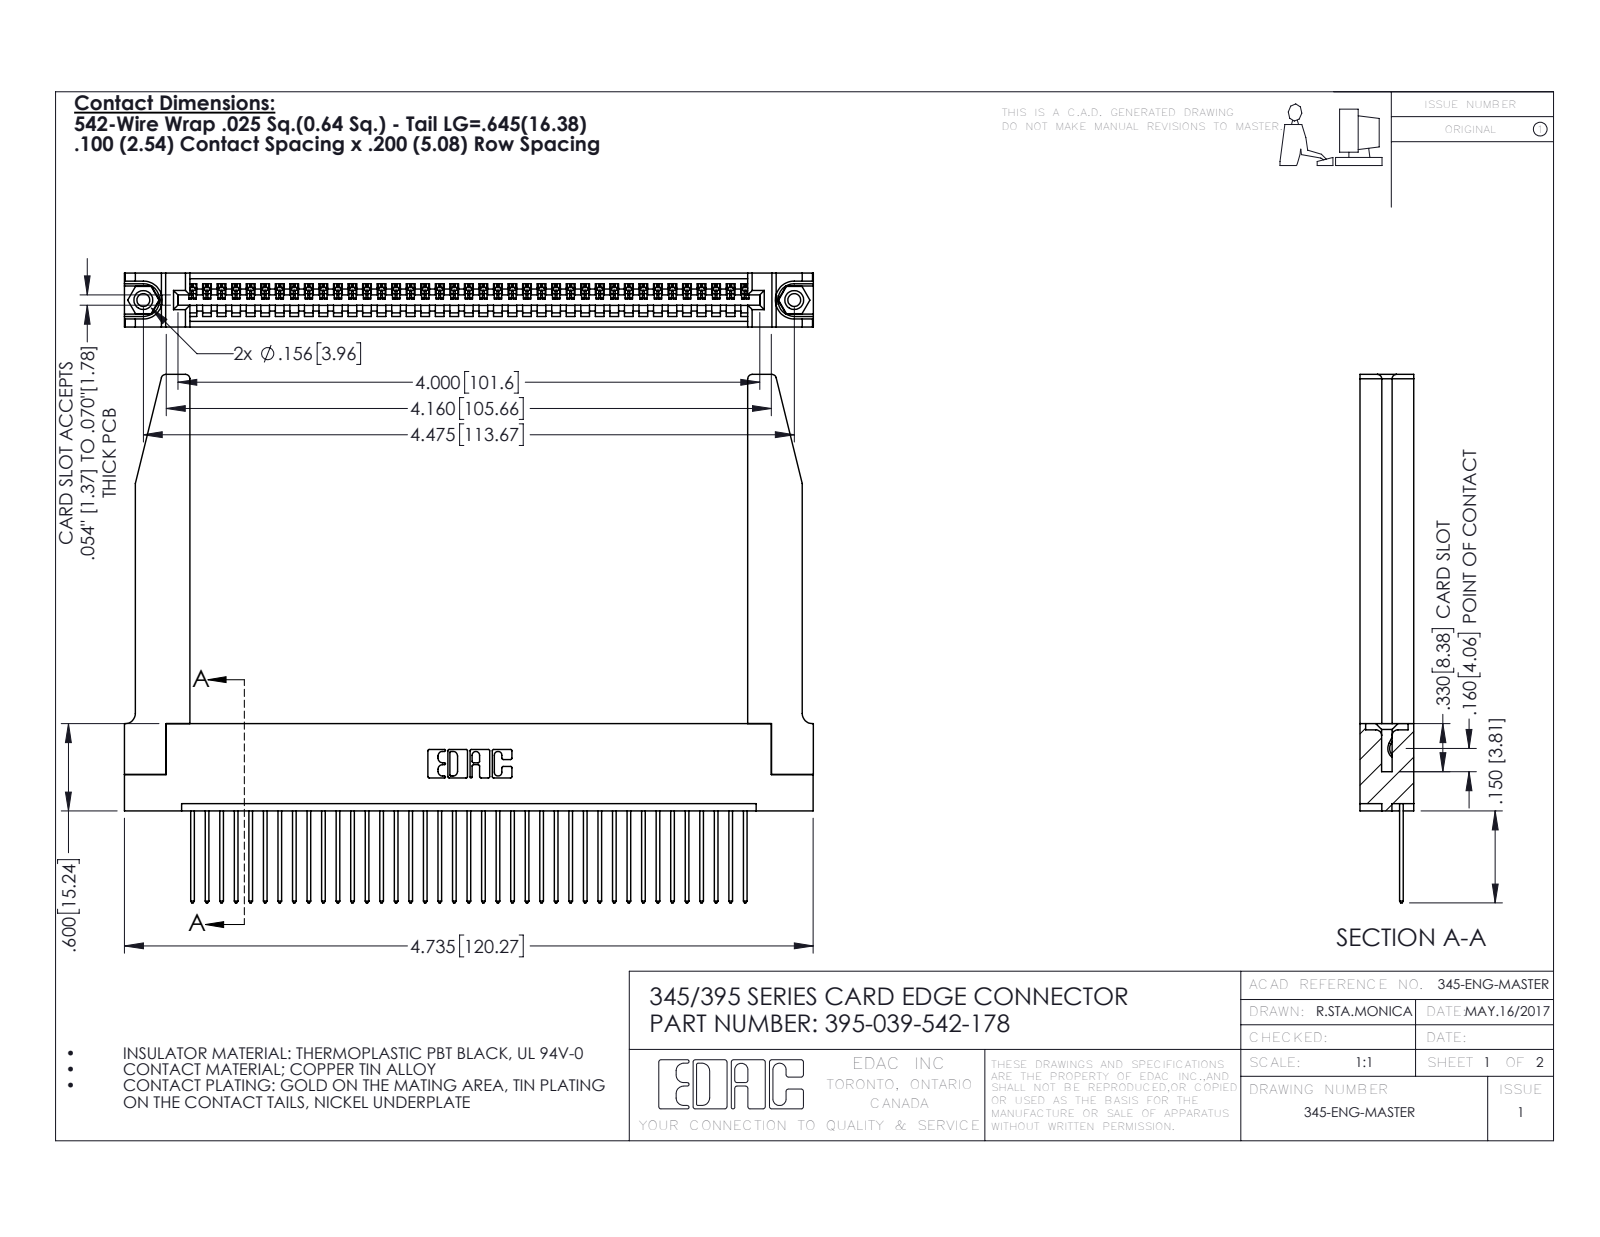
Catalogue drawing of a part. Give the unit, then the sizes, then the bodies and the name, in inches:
Units: inches
Overall size (bounding box): 4.736 × 3.632 × 0.37
Round holes (diameter × count): ⌀0.089 ×2, ⌀0.125 ×2, ⌀0.156 ×2, ⌀0.064 ×1
Round bosses / shafts (diameter × count): ⌀0.155 ×2
Partial cylindrical surfaces — rounded edges, fillets, slot ends (radius × count): R0.006 ×78, R0.01 ×78, R0.01 ×22, R0.03 ×8, R0.007 ×6, R0.031 ×6, R0.026 ×3, R0.031 ×2
Main face-to-face distances: 0.37, 0.072, 0.298, 0.2, 0.098, 0.272, 0.025, 0.225, 0.148, 0.15
Hole centre spacings: 0.27, 4.239, 4.475
Volume: 1.175 in³ · Surface area: 35.06 in²
Bodies: 44 solids, 2622 faces (1782 planar, 788 cylindrical, 52 other)
Part name (STEP PRODUCT): 345-292-001_345-293-142; 345 Part_Flush Mounting Lugs - 0.156 Dia-TH; 395-039-542-178; 345-220-078_345-220-078 (+1 more)
STEP written by: SolidWorks 2016 (CONFIG_CONTROL_DESIGN)
